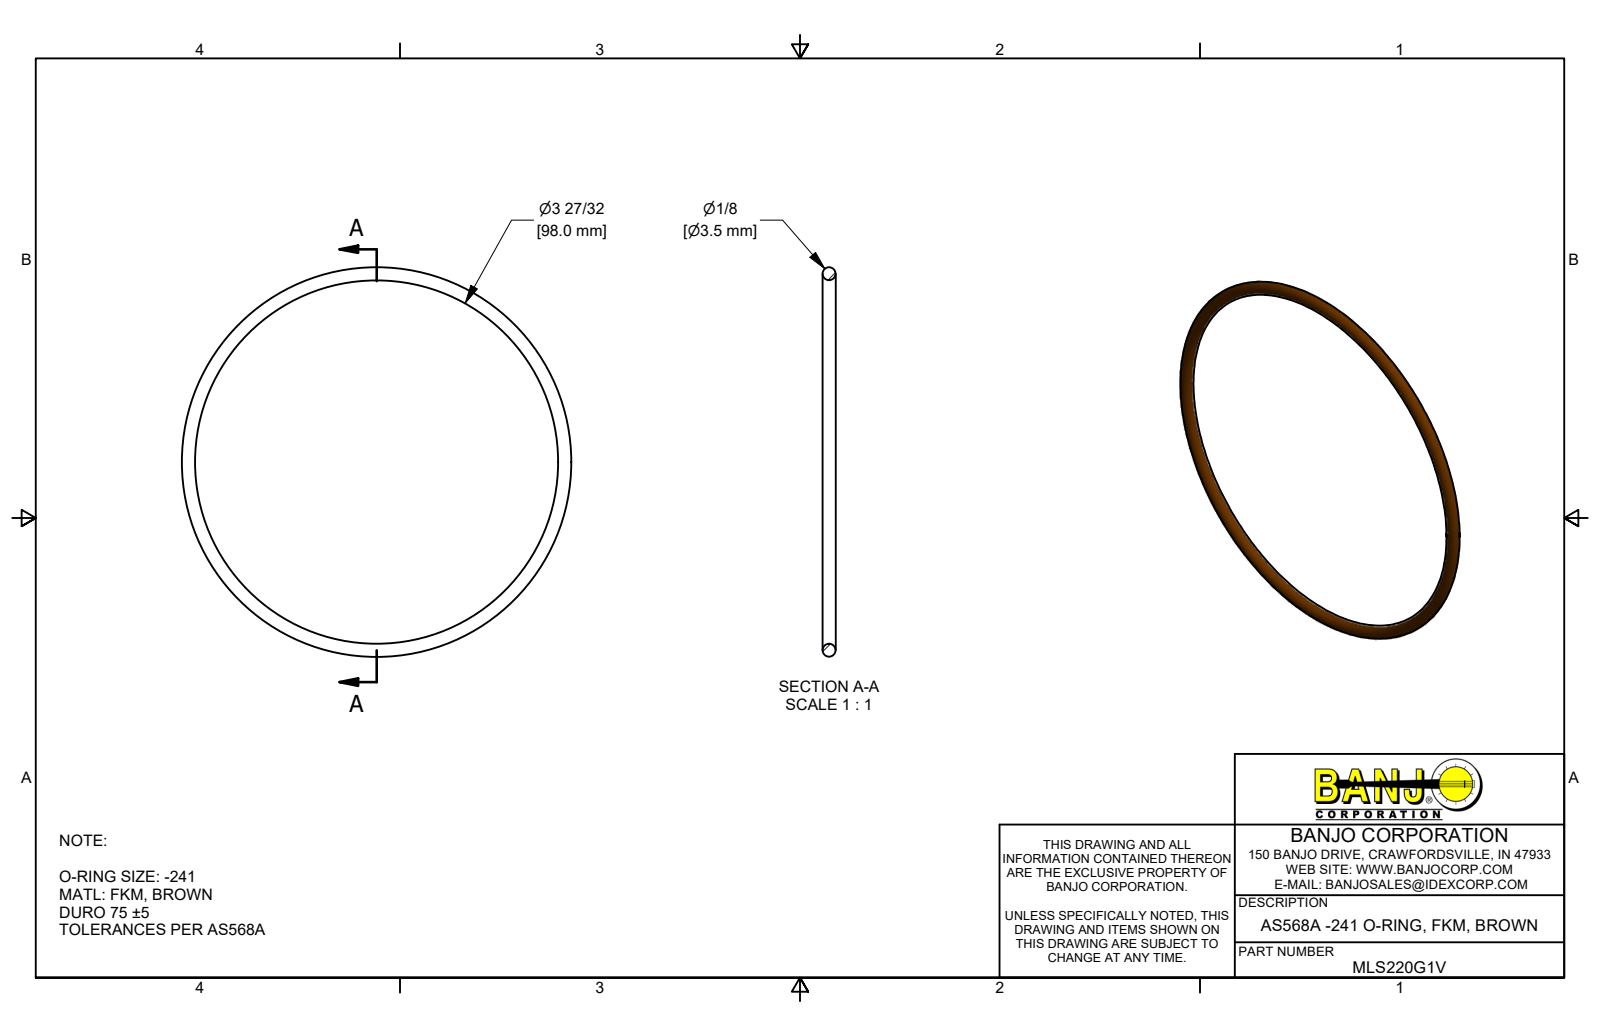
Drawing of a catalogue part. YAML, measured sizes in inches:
part_name: "MLS220G1V"
step_written_by: "Autodesk Inventor 2019 (AUTOMOTIVE_DESIGN)"
units: inches
bodies: {solids: 1, faces: 1, planar: 0, cylindrical: 0, other: 1}
overall_size: [4.137, 4.137, 0.139]
volume: 0.191
surface_area: 5.485
